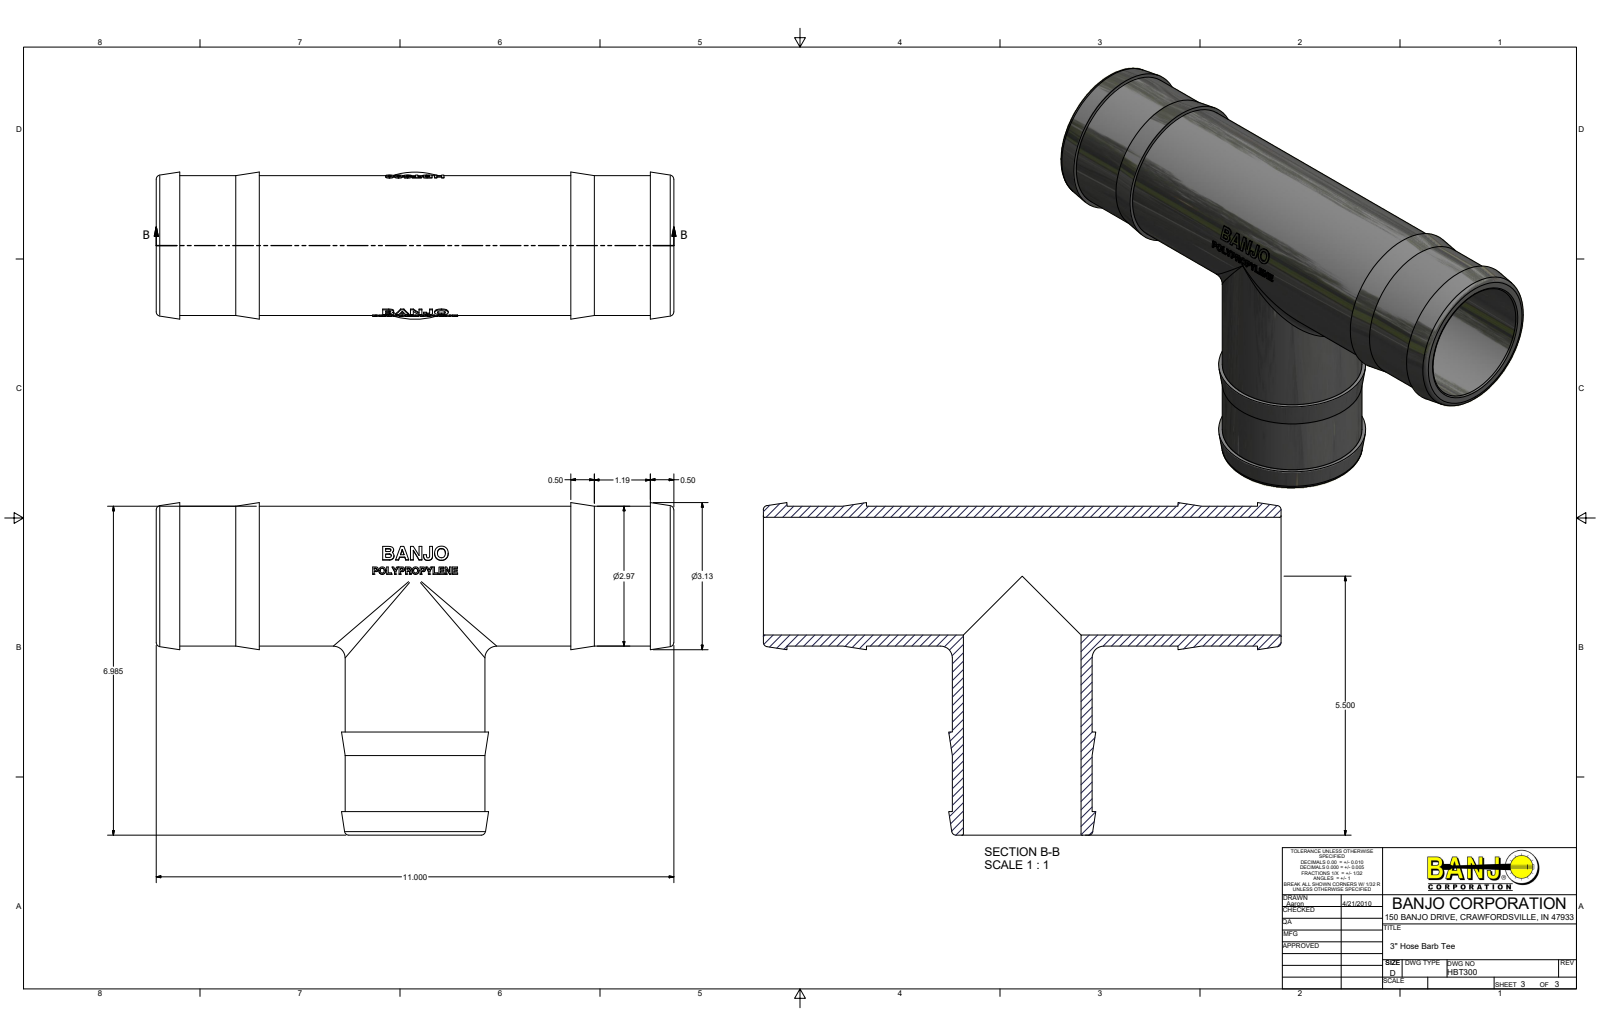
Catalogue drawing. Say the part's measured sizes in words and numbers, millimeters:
The part is named "HBT300". Its 3-D file was written by "Autodesk Inventor 2017 (AUTOMOTIVE_DESIGN)". It is 1 solid with 367 faces: 158 planar, 45 cylindrical and 164 other. Overall it measures 279.4 by 179.39 by 79.38 millimeters. Its volume is 506 643 cubic millimeters and its surface area 170 351 square millimeters. Round holes: 2 of diameter 63.5. Round bosses or shafts: 2 of diameter 75.44. Partial cylindrical surfaces (rounded edges, fillets, slot ends): 1 of radius 38.23. The main face-to-face distances are 12.7, 55.63, 42.93, 223.77, 266.7, 211.07, 279.4, 254, 168.14, 1.57.
